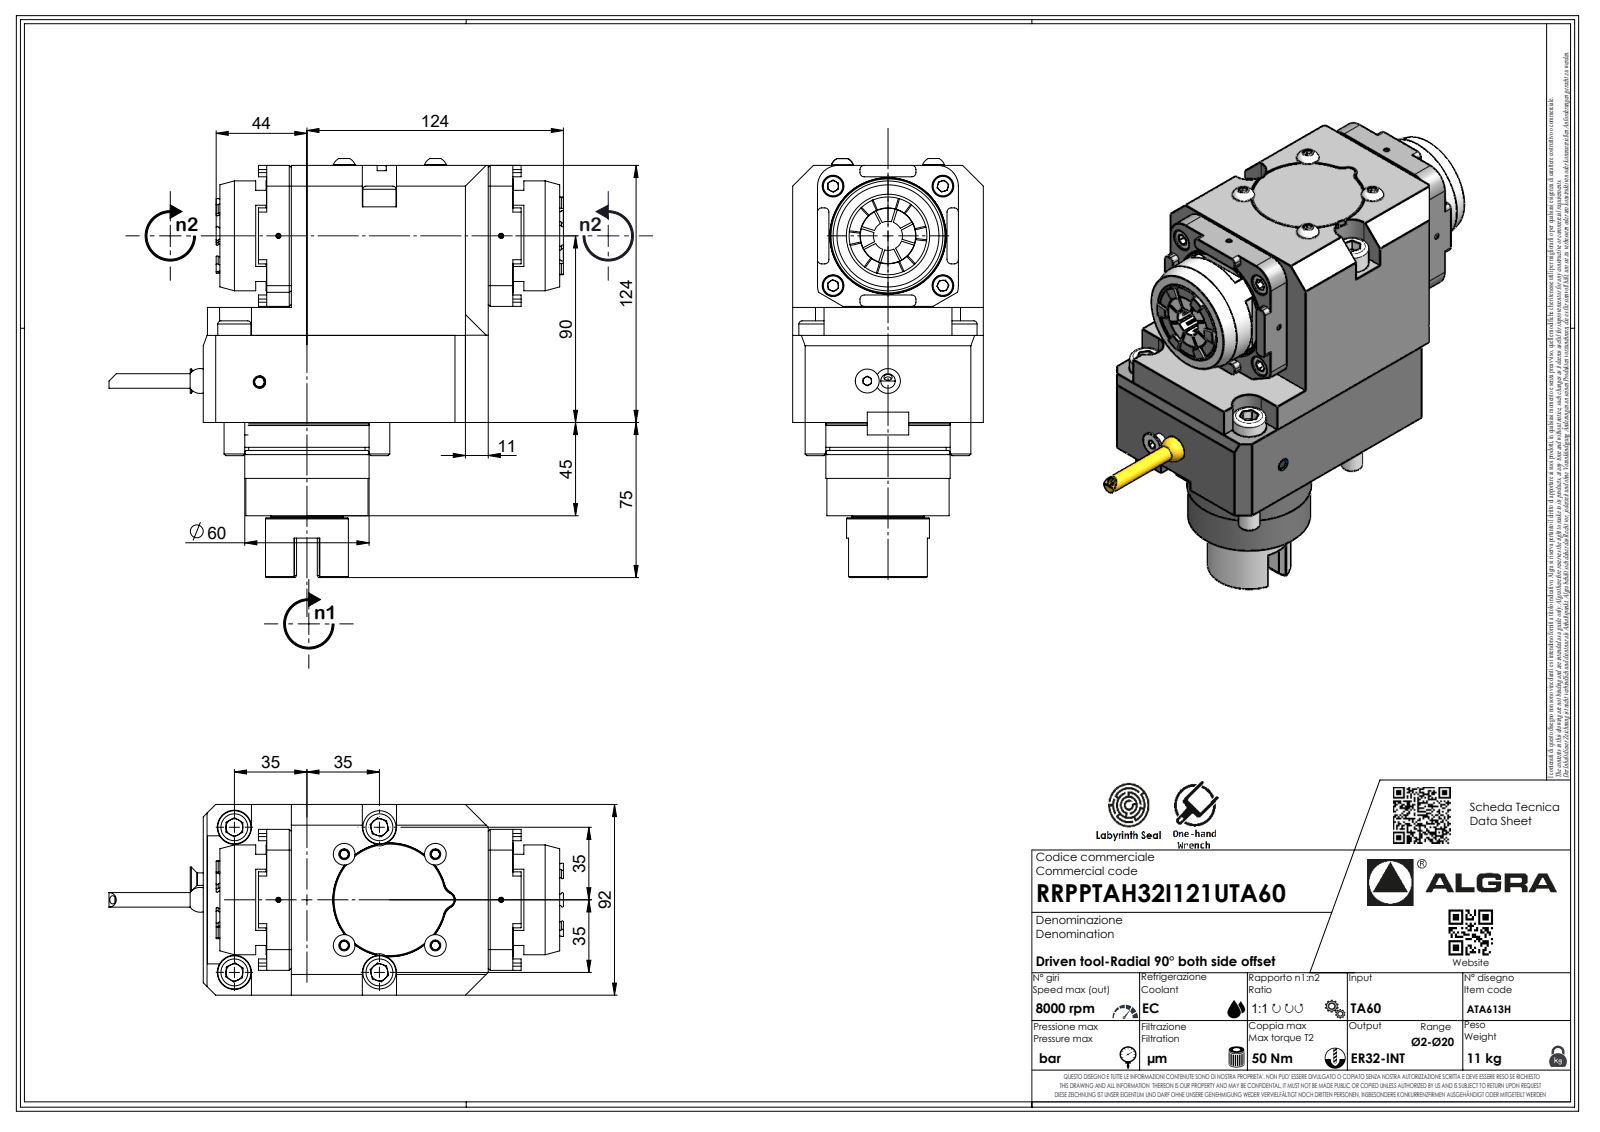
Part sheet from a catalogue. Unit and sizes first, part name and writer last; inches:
Units: inches
Overall size (bounding box): 7.957 × 6.772 × 3.622
Round holes (diameter × count): ⌀0.083 ×1
Round bosses / shafts (diameter × count): ⌀0.413 ×4, ⌀0.394 ×4, ⌀0.63 ×2, ⌀2.362 ×1, ⌀2.346 ×1, ⌀2.323 ×1, ⌀2.213 ×1, ⌀2.087 ×1
Partial cylindrical surfaces — rounded edges, fillets, slot ends (radius × count): R0.079 ×16, R0.013 ×7, R0.02 ×7, R0.146 ×7, R0.394 ×4, R0.197 ×2, R0.325 ×2, R0.008 ×1
Main face-to-face distances: 3.622, 4.882, 0.472, 2.677, 1.358, 5.098, 0.89, 5.567, 4.98, 2.185
Volume: 97.27 in³ · Surface area: 165.6 in²
Bodies: 1 solid, 596 faces (398 planar, 91 cylindrical, 107 other)
Part name (STEP PRODUCT): RRPPTAH32I121UTA60
STEP written by: SolidWorks 2023 (AUTOMOTIVE_DESIGN)
